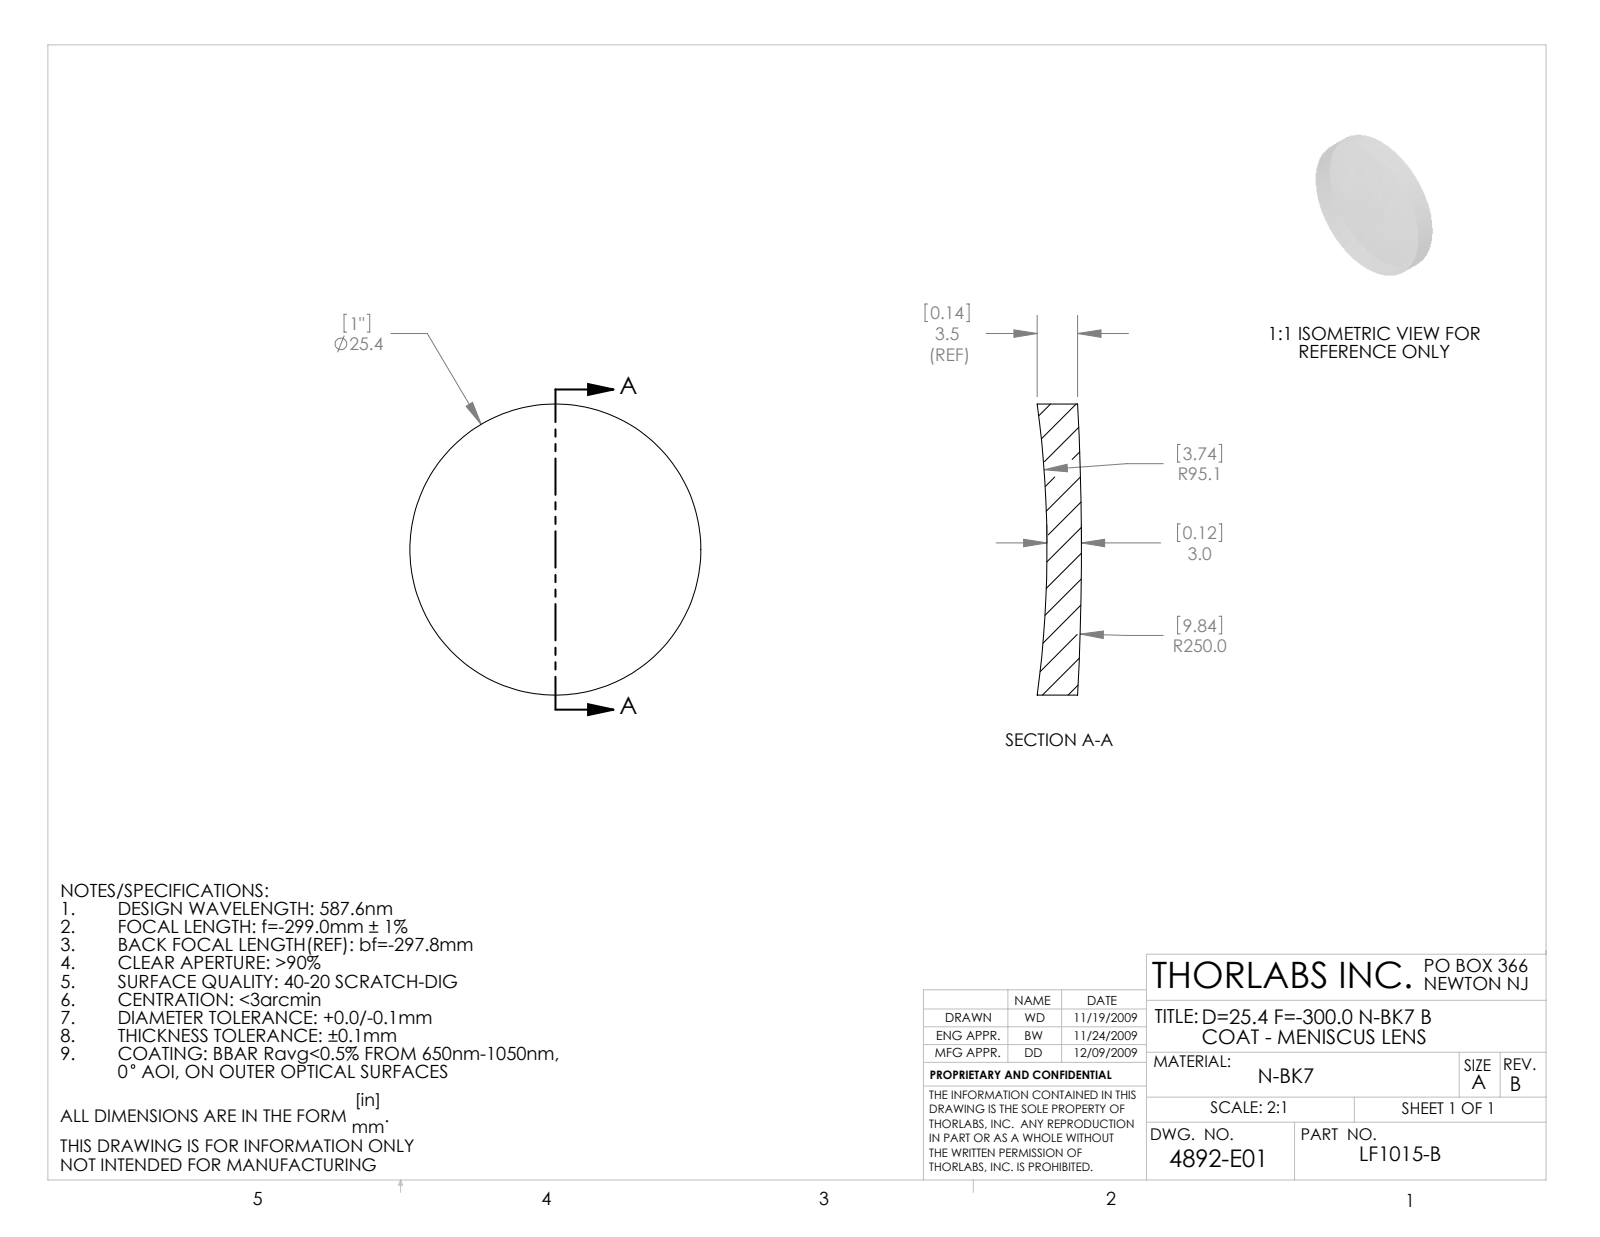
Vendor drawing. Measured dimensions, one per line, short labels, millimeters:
name: 4892-E0W
written by: SolidWorks 2009 (AUTOMOTIVE_DESIGN)
unit: mm
bodies: 1 solid, 6 faces (0 planar, 2 cylindrical, 4 other)
size: 25.4 × 25.4 × 3.85
volume: 1 654 mm³; area: 1 298 mm²
bosses: 1× ⌀25.4
